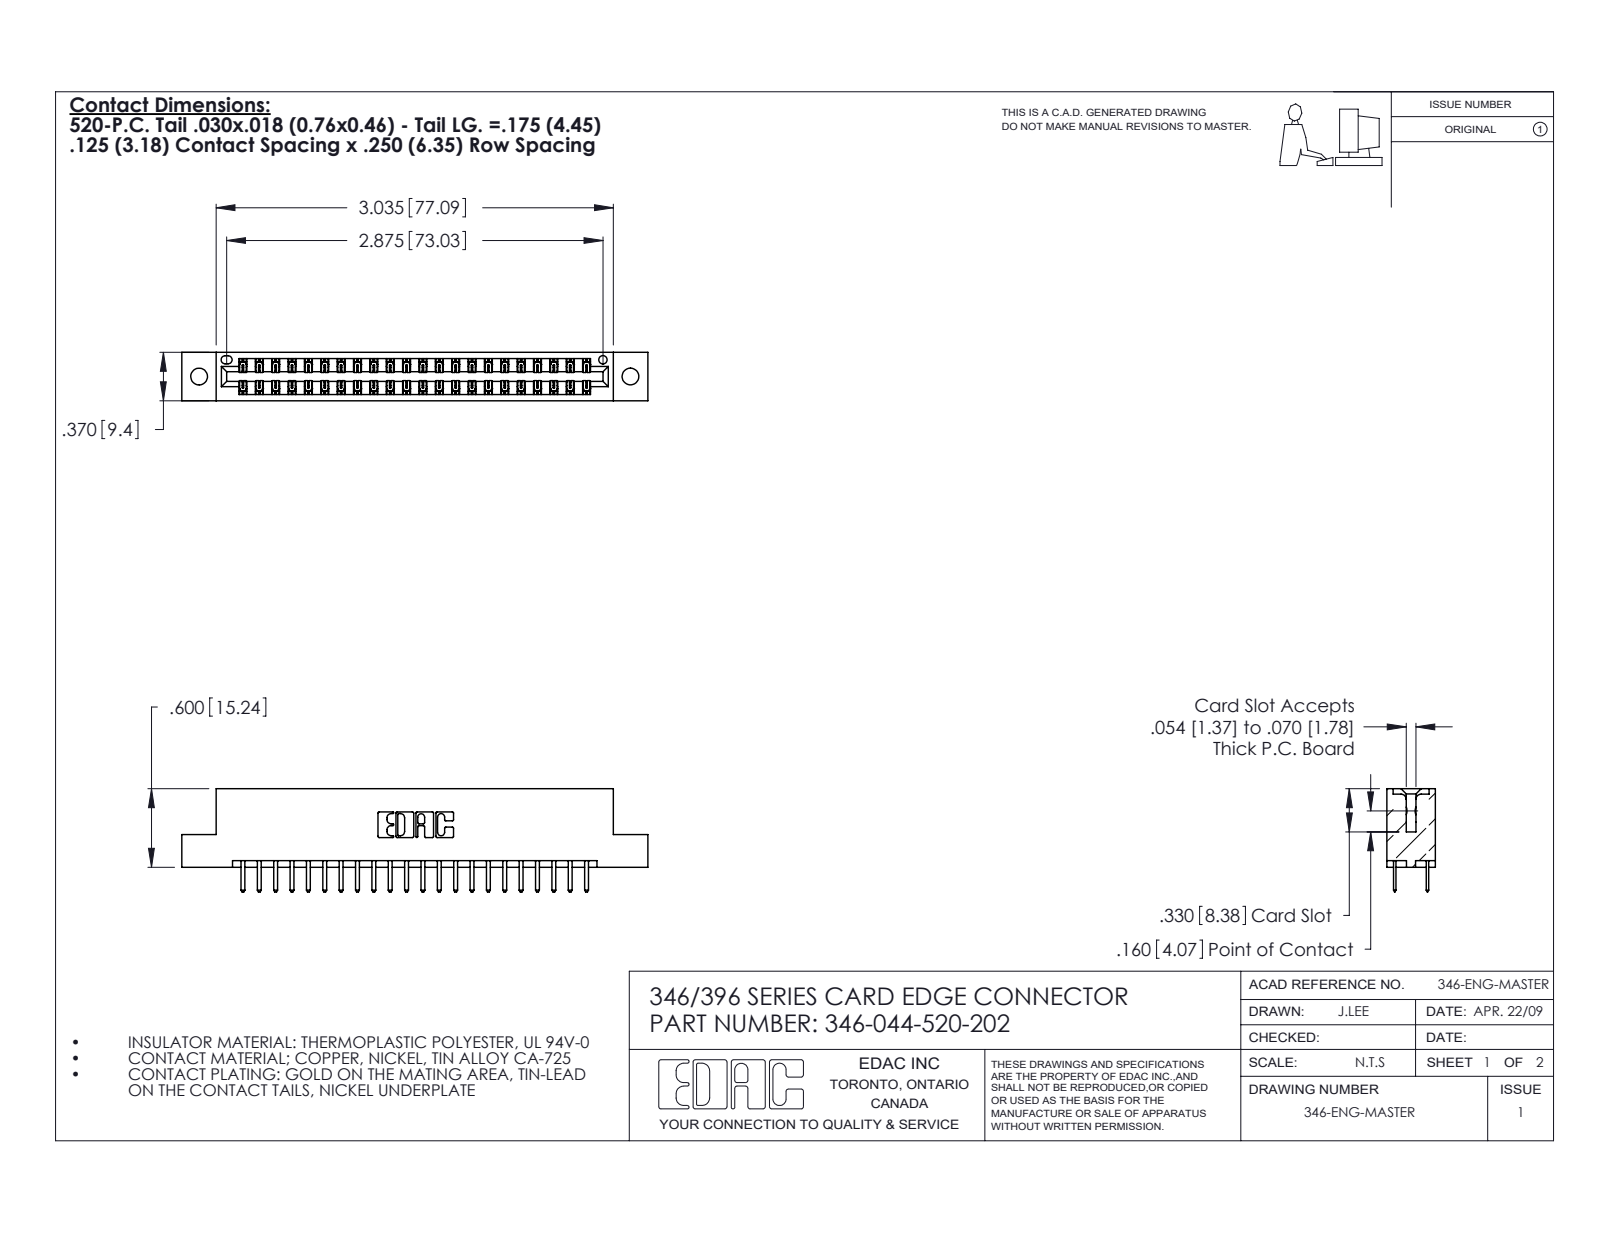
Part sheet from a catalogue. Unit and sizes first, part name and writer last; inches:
Units: inches
Overall size (bounding box): 3.56 × 0.788 × 0.37
Round holes (diameter × count): ⌀0.128 ×2, ⌀0.064 ×1
Partial cylindrical surfaces — rounded edges, fillets, slot ends (radius × count): R0.006 ×66, R0.01 ×48, R0.01 ×22, R0.007 ×6, R0.031 ×6, R0.026 ×3, R0.014 ×2, R0.022 ×2
Main face-to-face distances: 0.048, 0.322, 0.25, 0.37, 0.275, 0.072, 0.298, 0.025, 0.148, 0.222
Hole centre spacings: 0.246, 3.087, 3.295
Volume: 0.525 in³ · Surface area: 17.36 in²
Bodies: 45 solids, 2586 faces (1704 planar, 882 cylindrical, 0 other)
Part name (STEP PRODUCT): 345-292-001_345-293-120; 346 Part_Flush Mounting Lugs - 0.128 Dia; 346-044-520-202
STEP written by: SolidWorks 2020 (CONFIG_CONTROL_DESIGN)
